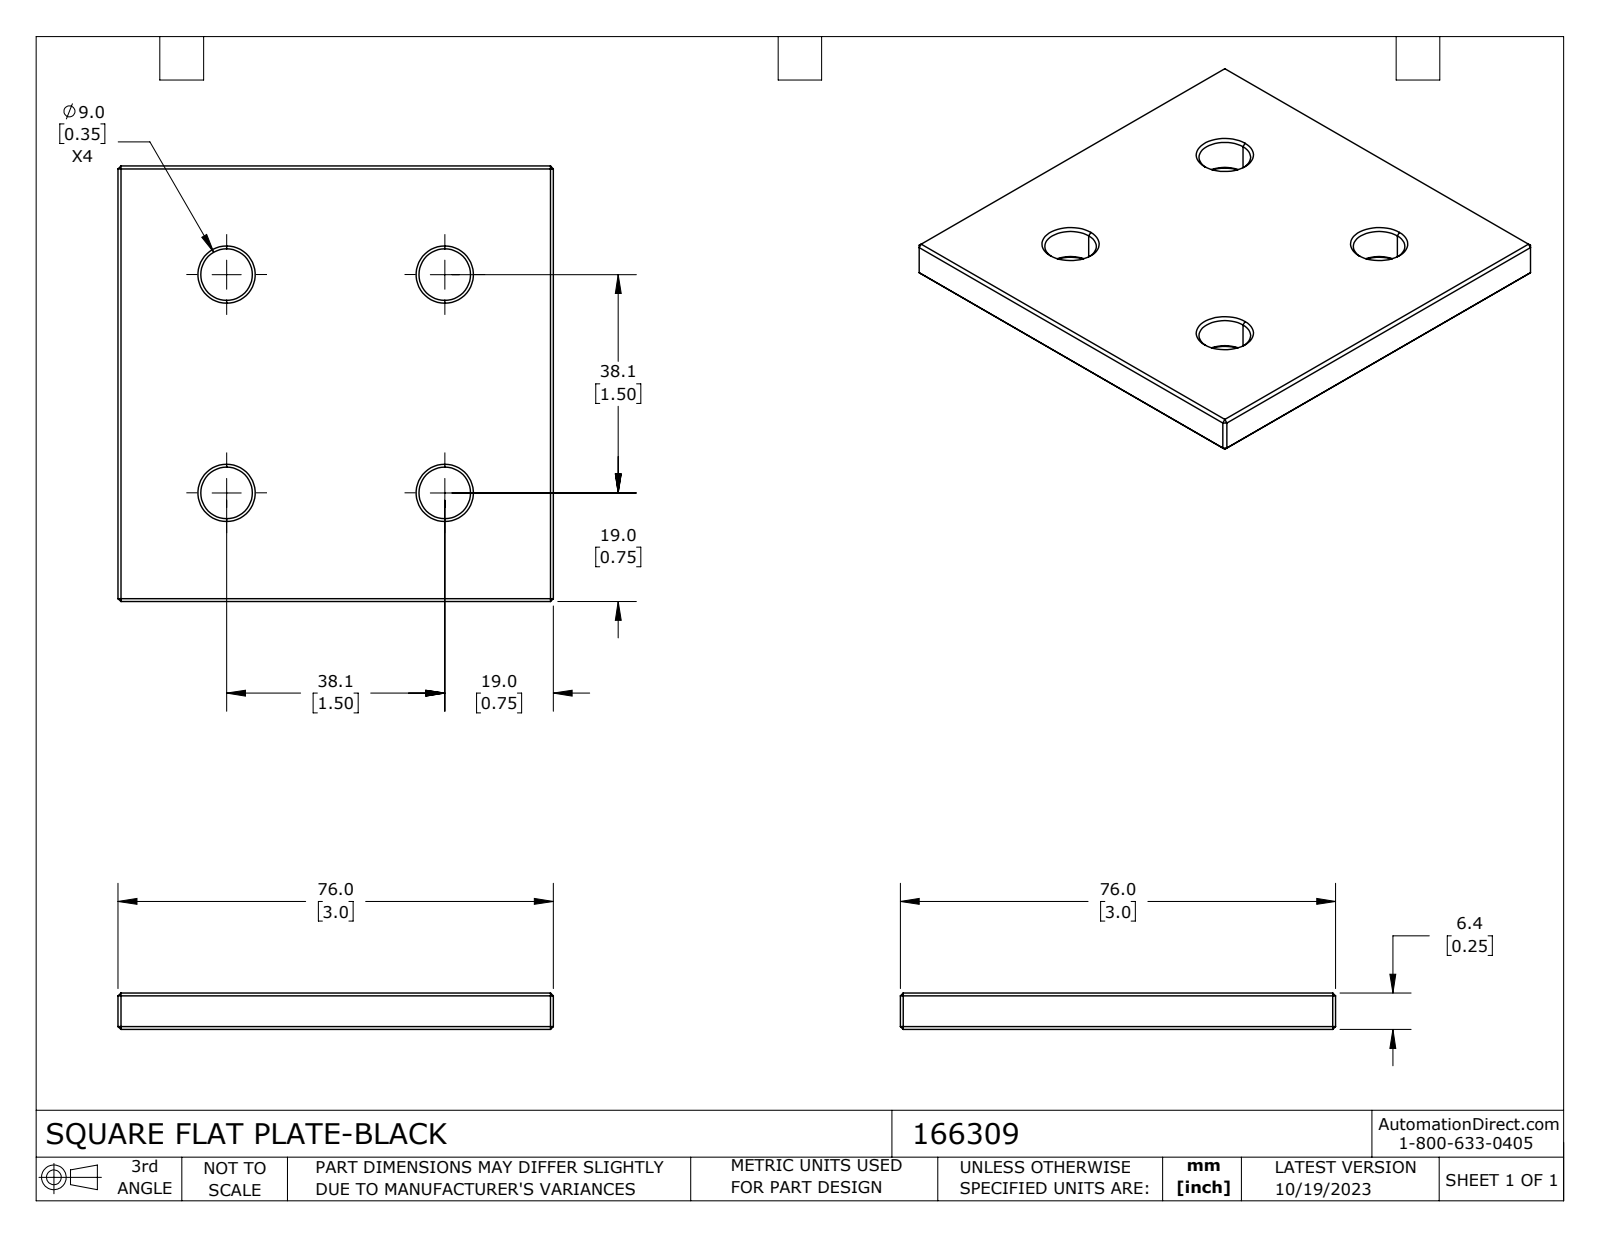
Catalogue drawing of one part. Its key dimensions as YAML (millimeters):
part_name: "166309"
step_written_by: "SolidWorks 2023 (CONFIG_CONTROL_DESIGN)"
units: millimeters
bodies: {solids: 1, faces: 50, planar: 26, cylindrical: 8, other: 16}
overall_size: [76, 76, 6.35]
volume: 34954
surface_area: 13442
round_holes:
  - {diameter: 9, count: 4}
face_to_face_distances: [6.35, 76, 57.51, 106.76, 90.21]
hole_center_spacings: [38.1, 53.88]
